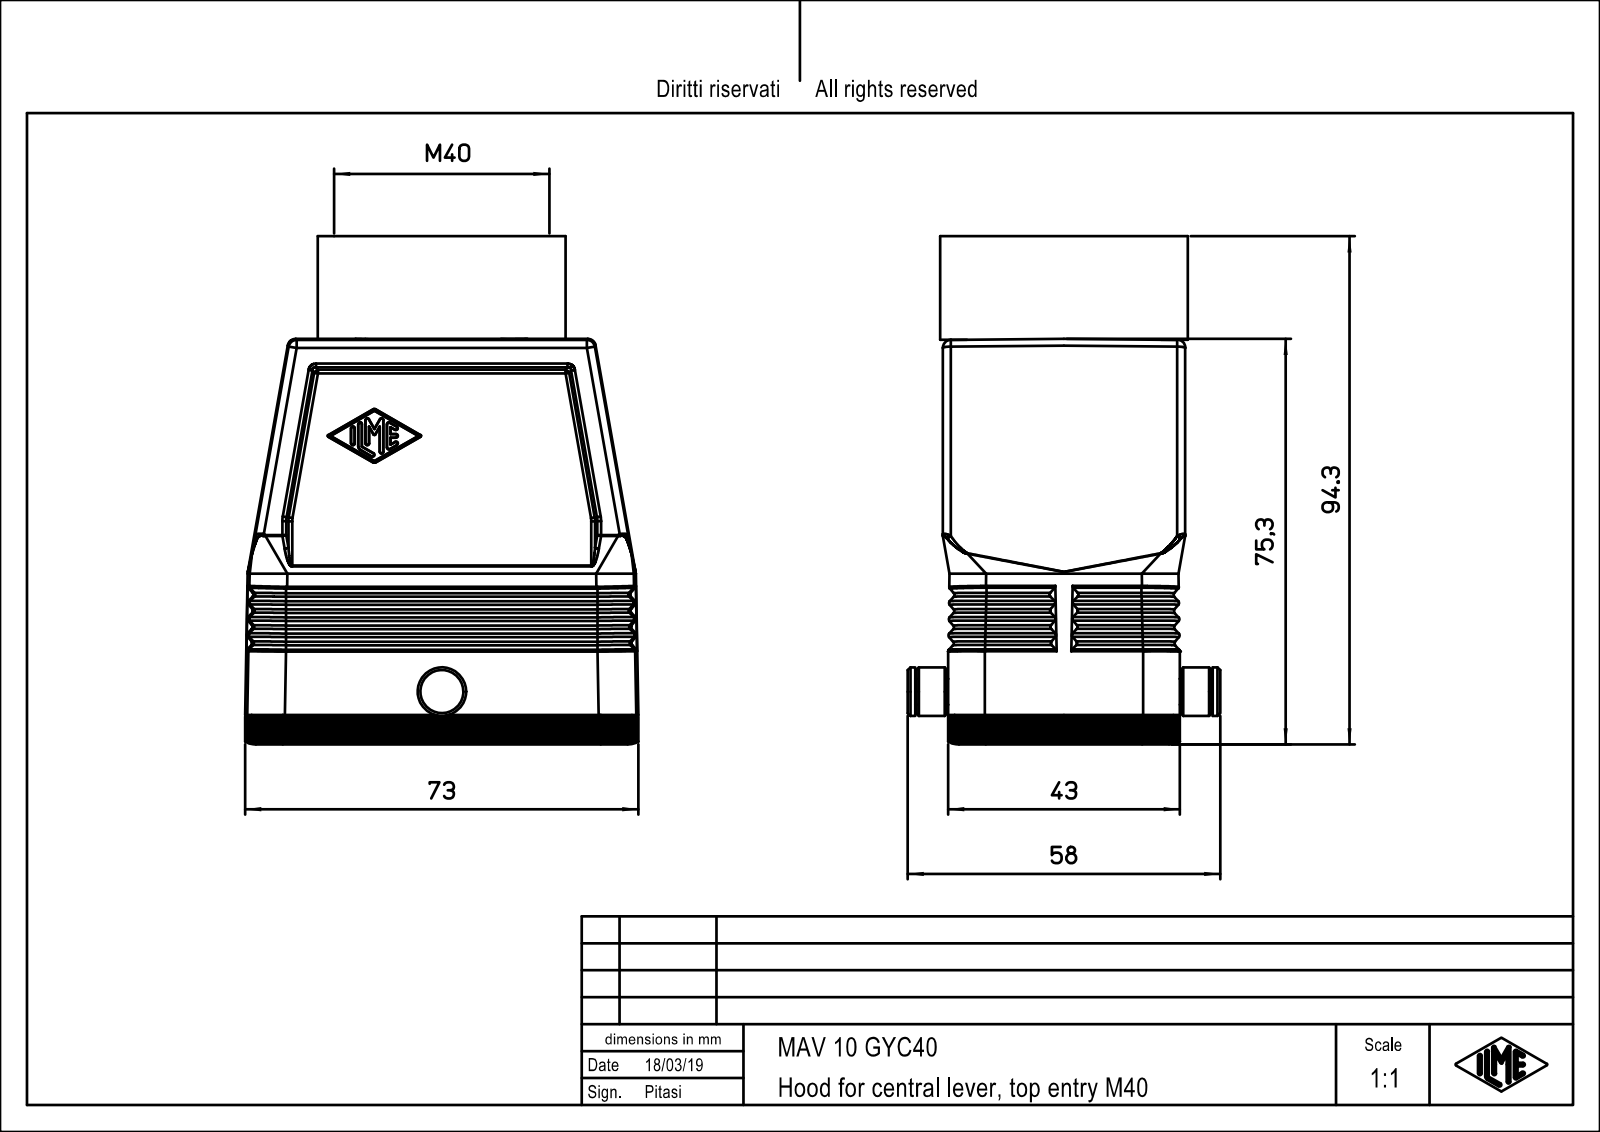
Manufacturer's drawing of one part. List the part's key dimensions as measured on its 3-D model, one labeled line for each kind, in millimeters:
Part name (STEP PRODUCT): MAV_10_GYC40
STEP written by: PTC Creo Elements/Direct Modeling 19.0E 27-Jun-2016 (C) Parametric Technology GmbH (AUTOMOTIVE_DESIGN)
Units: millimetres
Bodies: 1 solid, 506 faces (162 planar, 144 cylindrical, 200 other)
Overall size (bounding box): 94.25 × 73 × 58
Volume: 84 419 mm³ · Surface area: 42 176 mm²
Round holes (diameter × count): ⌀3 ×4, ⌀34 ×1
Round bosses / shafts (diameter × count): ⌀46 ×1, ⌀40 ×1, ⌀9 ×1, ⌀4.8 ×1
Partial cylindrical surfaces — rounded edges, fillets, slot ends (radius × count): R1 ×32, R0.5 ×16, R7 ×12, R1.5 ×10, R3 ×8, R3.5 ×4, R4 ×4, R4.2 ×4
Main face-to-face distances: 43, 4, 2, 1.05, 7, 6, 1, 44, 39, 11.5
Hole centre spacings: 31.54, 27, 57, 63.07
